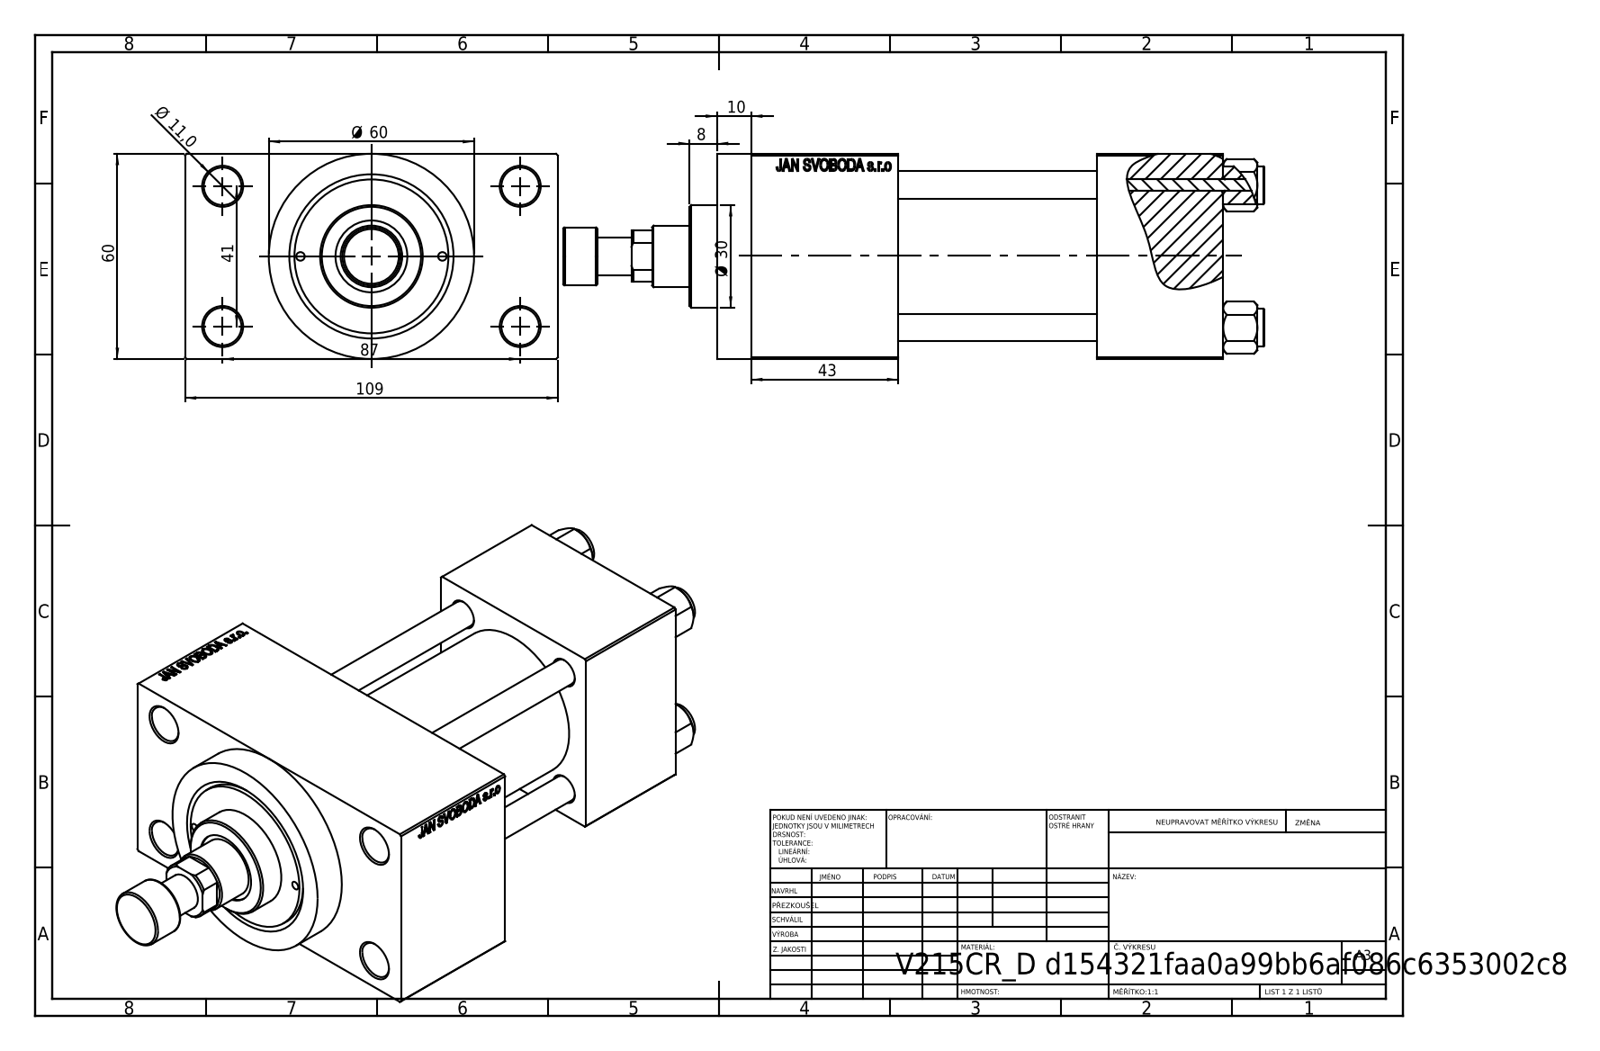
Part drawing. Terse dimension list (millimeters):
name: NUT_M5_D; V215CR_ROD_END_F; V215CR_VCP_D; V215CR_D_Body (+2 more)
written by: SolidWorks 2019 (CONFIG_CONTROL_DESIGN)
unit: mm
bodies: 12 solids, 1123 faces (503 planar, 96 cylindrical, 524 other)
size: 205 × 109 × 60
volume: 515 525 mm³; area: 123 814 mm²
holes: 4× ⌀8, 4× ⌀11, 2× ⌀2.5, 2× ⌀7, 2× ⌀16.66, 2× ⌀24, 1× ⌀8.5, 1× ⌀18, 1× ⌀21, 1× ⌀31, 1× ⌀40, 1× ⌀45
bosses: 5× ⌀11, 1× ⌀60, 1× ⌀46, 1× ⌀30, 1× ⌀17
face distances: 60, 58, 24.5, 37, 84.5, 95, 138, 101, 43, 10
hole spacings: 20.85, 22.65, 29.49, 30.62, 41.7, 46.53, 47.15, 48.09
